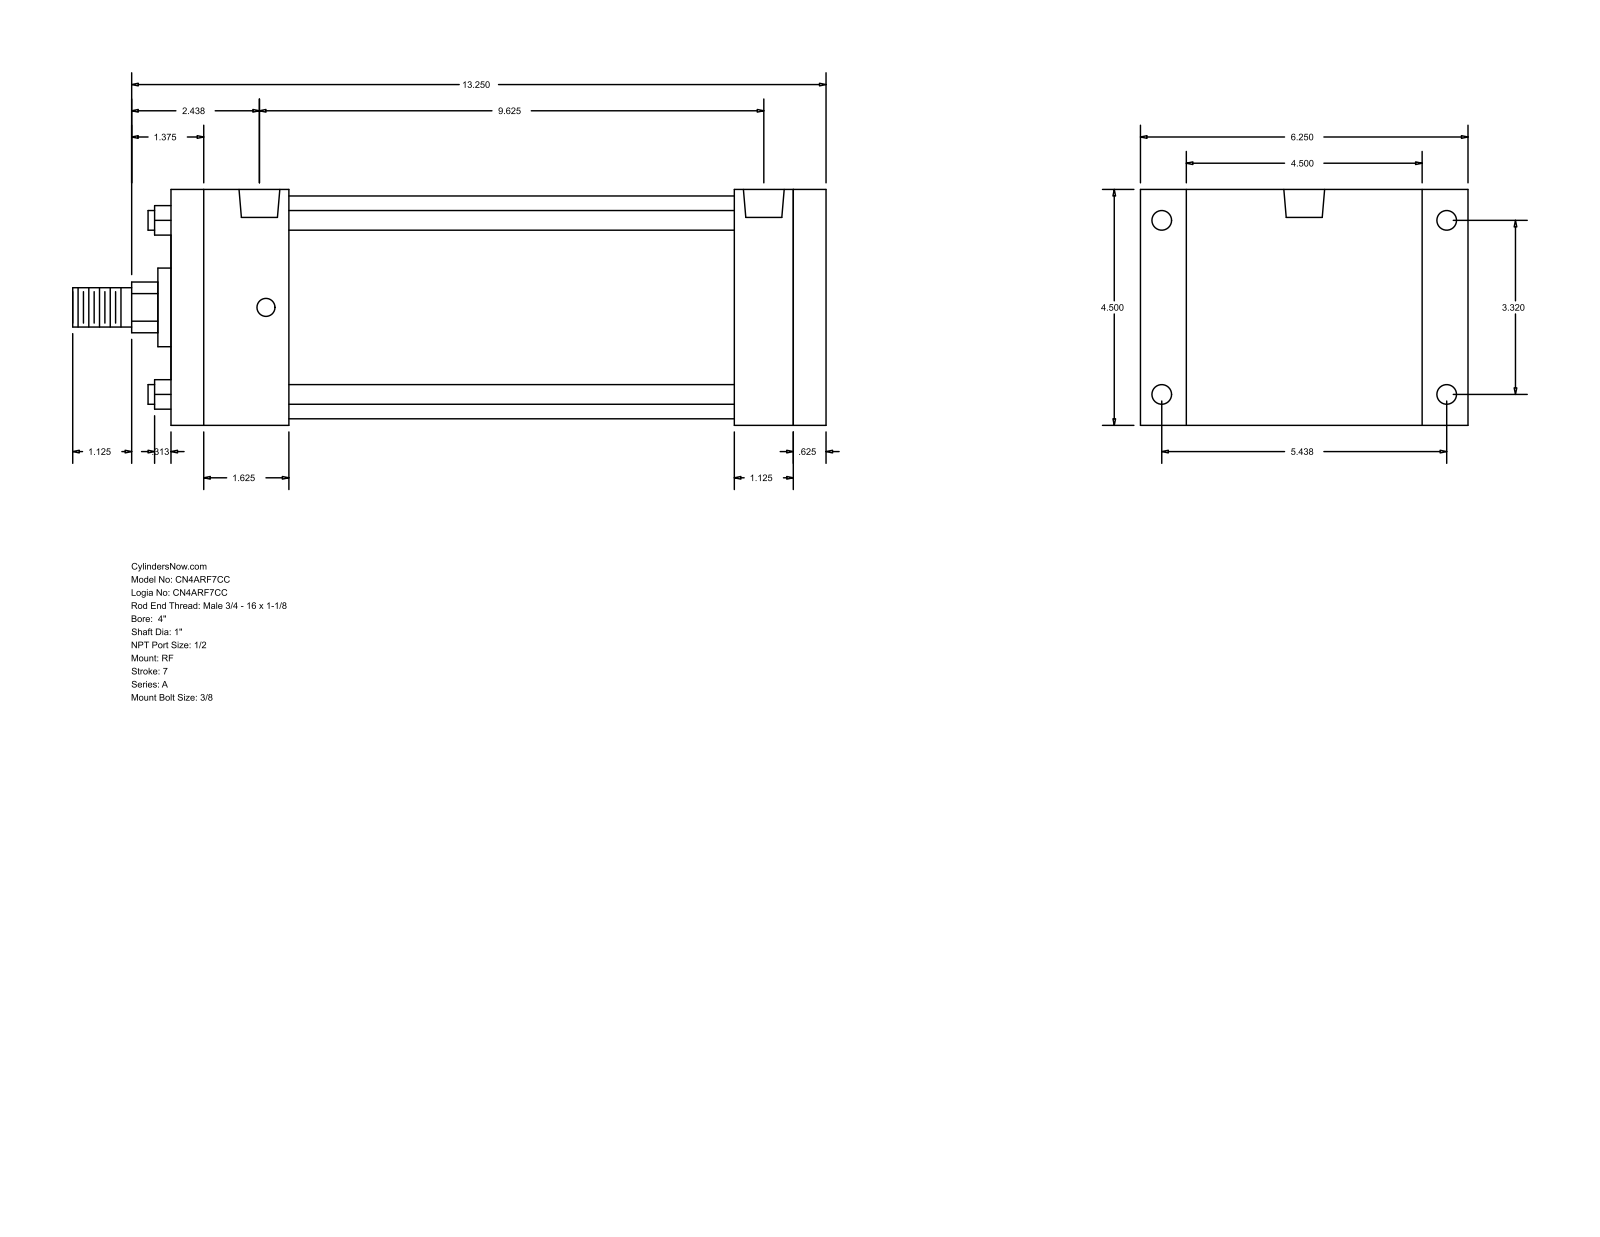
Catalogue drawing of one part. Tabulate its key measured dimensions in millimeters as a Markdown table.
| quantity | value |
| --- | --- |
| part name | A_RF__0400_1 |
| STEP written by | GSSL Pune (CONFIG_CONTROL_DESIGN) |
| units | millimeters |
| bodies | 0 solids, 92 faces (64 planar, 28 cylindrical, 0 other) |
| overall size | 365.12 × 158.75 × 114.3 |
| round holes (diameter × count) | 8.73 × 4, 9.53 × 4, 19.77 × 2 |
| round bosses / shafts (diameter × count) | 9.53 × 4, 107.95 × 1, 38.1 × 1, 25.4 × 1, 19.05 × 1 |
| partial cylindrical surfaces (radius × count) | 12.29 × 1 |
| main face-to-face distances | 114.3, 317.5, 301.63, 15.87, 22.23, 136.53, 273.05, 28.58, 44.45, 57.15 |
| hole center spacings | 3.18, 84.32, 138.12, 161.82, 238.12, 241.3, 244.48 |
